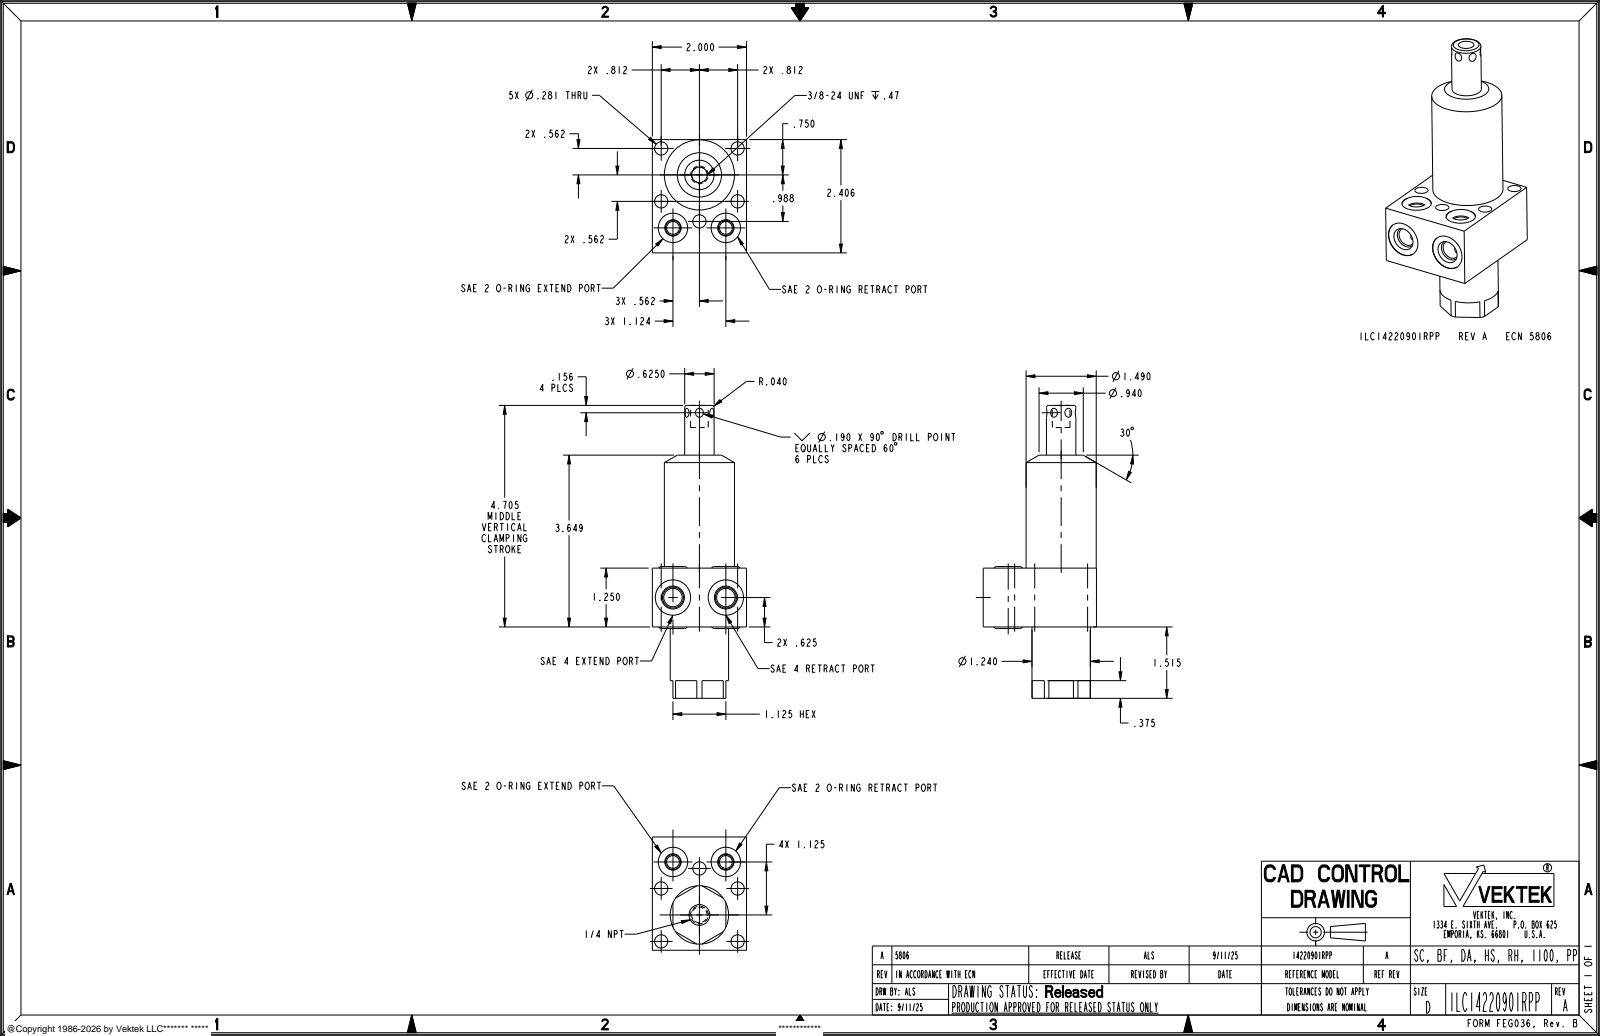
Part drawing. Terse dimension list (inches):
name: ILC14220901RPP
written by: CREO PARAMETRIC BY PTC INC, 2021164 (AUTOMOTIVE_DESIGN)
unit: in
bodies: 5 solids, 135 faces (31 planar, 46 cylindrical, 58 other)
size: 6.22 × 2.656 × 2.2
volume: 11.38 in³; area: 51.93 in²
holes: 5× ⌀0.281, 2× ⌀0.272, 2× ⌀0.392, 2× ⌀0.625, 2× ⌀0.75, 1× ⌀0.332, 1× ⌀0.44
bosses: 1× ⌀1.49, 1× ⌀1.24, 1× ⌀0.625, 1× ⌀0.375
face distances: 2, 1.25, 2.406, 1.515, 2.765, 0.105, 1.145, 1.125, 2.396, 2.66
hole spacings: 0.987, 1.124, 0.578, 0.616, 0.917, 1.257, 1.485, 1.624
